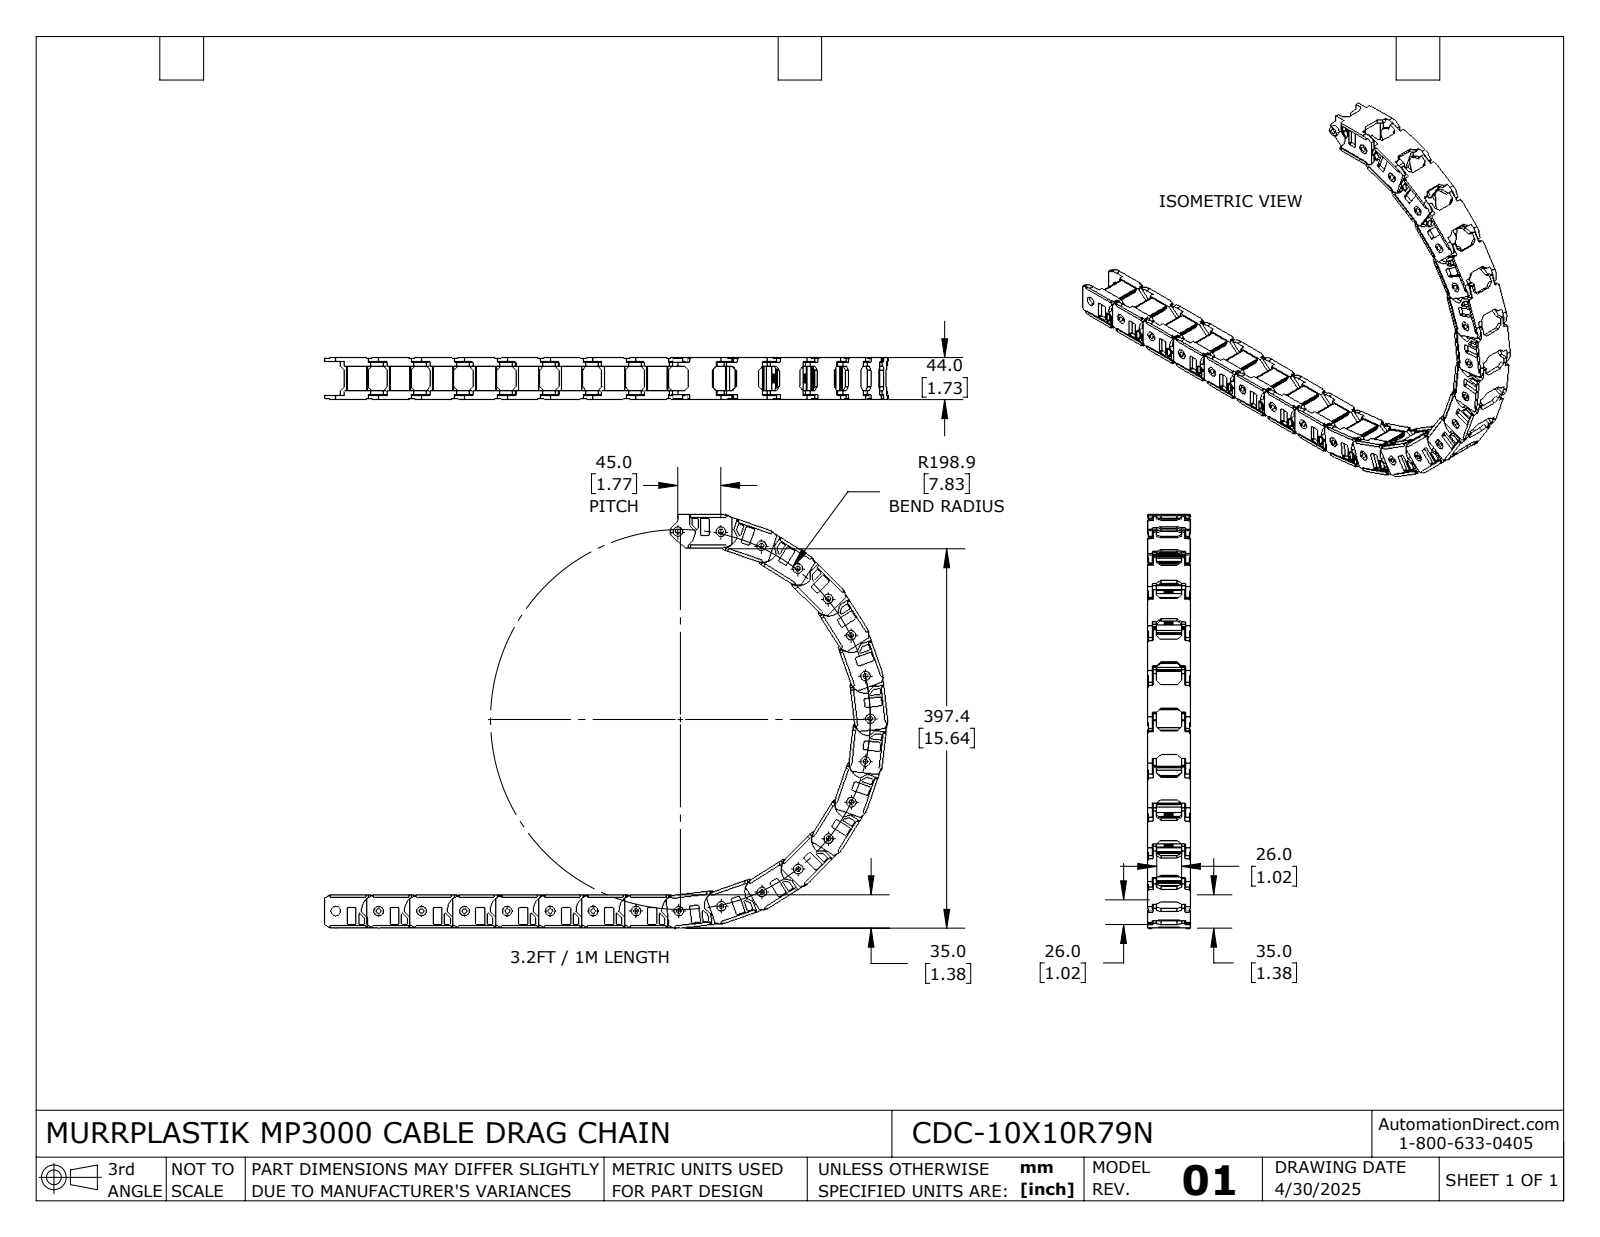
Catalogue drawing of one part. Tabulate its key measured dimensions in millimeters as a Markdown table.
| quantity | value |
| --- | --- |
| part name | CDC-10X10R79N |
| STEP written by | SolidWorks 2024 (AUTOMOTIVE_DESIGN) |
| units | millimeters |
| bodies | 22 solids, 3344 faces (2244 planar, 1100 cylindrical, 0 other) |
| overall size | 590.56 × 432.41 × 44 |
| volume | 546 930 mm³ |
| surface area | 321 003 mm² |
| round holes (diameter × count) | 5.1 × 22, 10.1 × 22 |
| round bosses / shafts (diameter × count) | 10 × 22 |
| partial cylindrical surfaces (radius × count) | 1 × 176, 0.5 × 88, 1.5 × 44, 2 × 44, 21 × 44, 2.8 × 22, 8 × 22, 18 × 22 |
| main face-to-face distances | 34, 8, 26, 33.8, 4, 30.3, 3.7, 38.3, 4.3, 3.5 |
| hole center spacings | 45, 44.98, 89.43, 89.4, 132.74, 174.37, 132.68, 132.72 |
